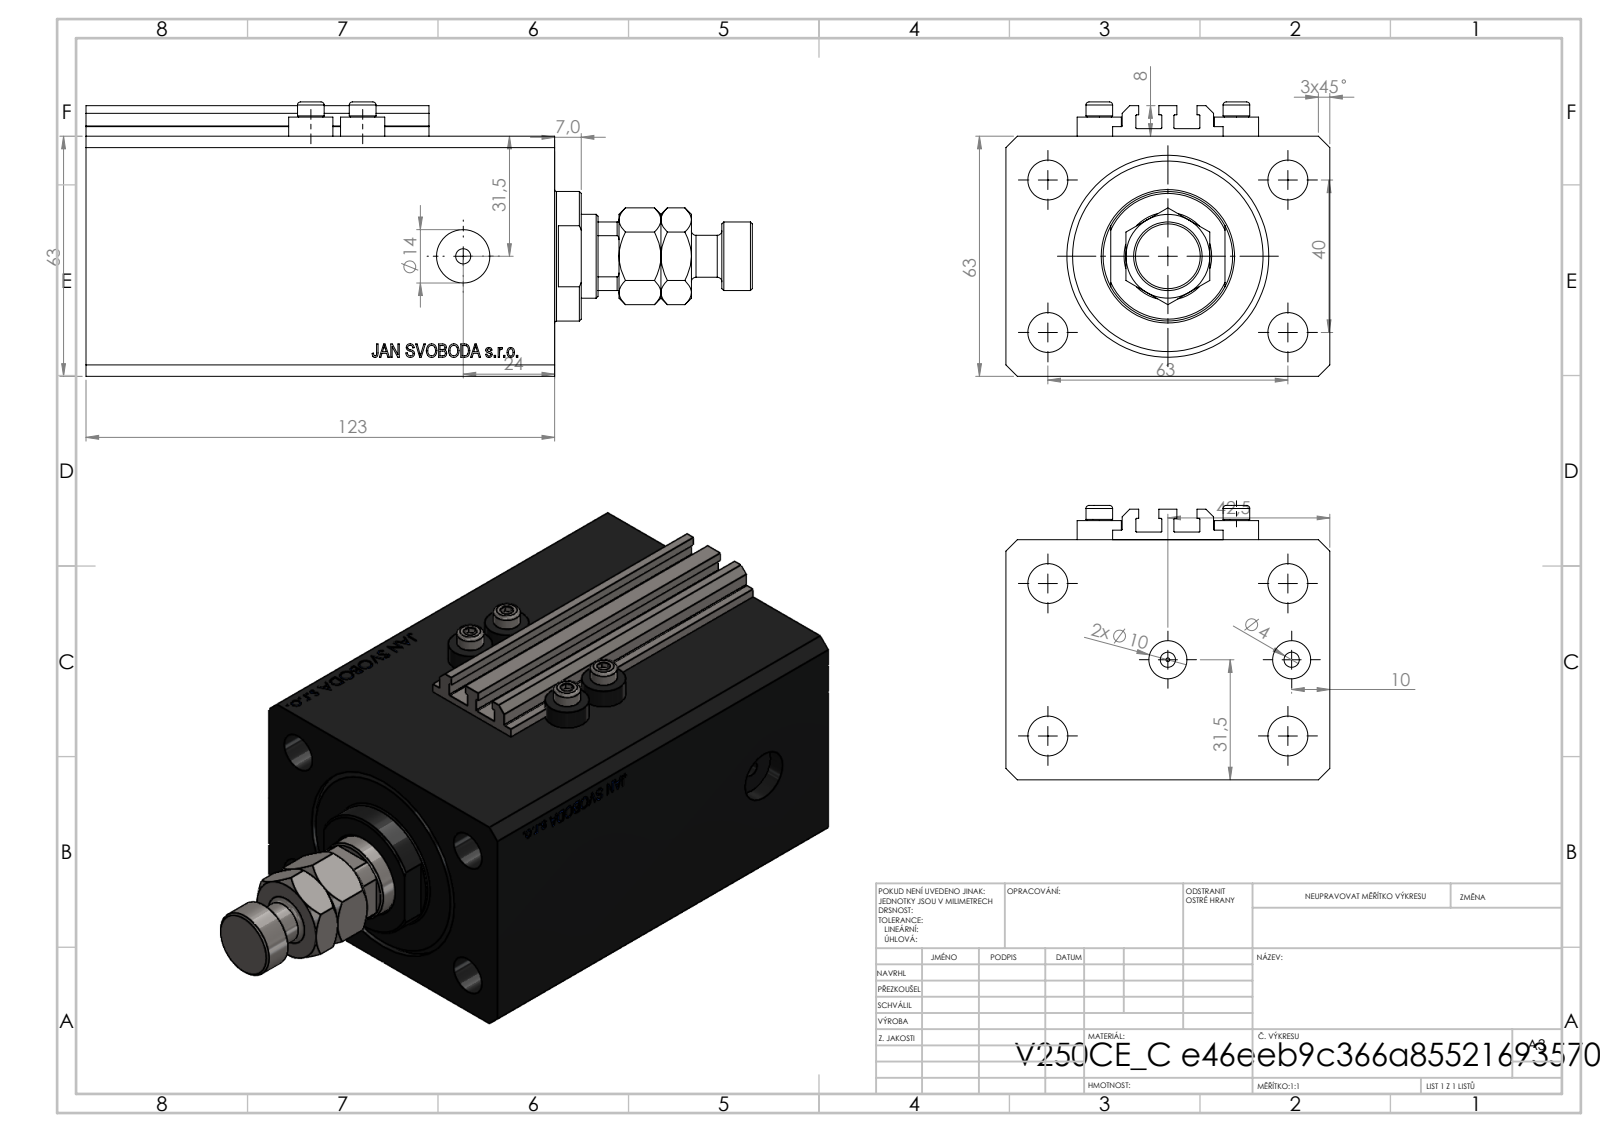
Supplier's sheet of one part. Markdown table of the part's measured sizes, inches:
| quantity | value |
| --- | --- |
| part name | MFA; ALLEN BOLT V250CE; V250CE_VC_C; V250CE_C (+1 more) |
| STEP written by | SolidWorks 2019 (CONFIG_CONTROL_DESIGN) |
| units | inches |
| bodies | 9 solids, 1090 faces (520 planar, 92 cylindrical, 478 other) |
| overall size | 6.886 × 3.346 × 2.835 |
| volume | 36.47 in³ |
| surface area | 185.3 in² |
| round holes (diameter × count) | 0.157 × 8, 0.413 × 4, 0.394 × 2, 0.551 × 2, 0.049 × 1, 0.492 × 1, 0.866 × 1, 1.575 × 1, 2.087 × 1 |
| round bosses / shafts (diameter × count) | 0.457 × 4, 0.276 × 4, 1.339 × 1, 0.709 × 1, 0.433 × 1 |
| partial cylindrical surfaces (radius × count) | 0.008 × 10, 0.413 × 1 |
| main face-to-face distances | 2.48, 3.346, 4.843, 3.776, 1.067, 0.449, 3.327, 4.394, 0.098, 0.079 |
| hole center spacings | 1.469, 0.535, 0.788, 1.417, 1.515, 1.575, 2.48, 2.64 |
